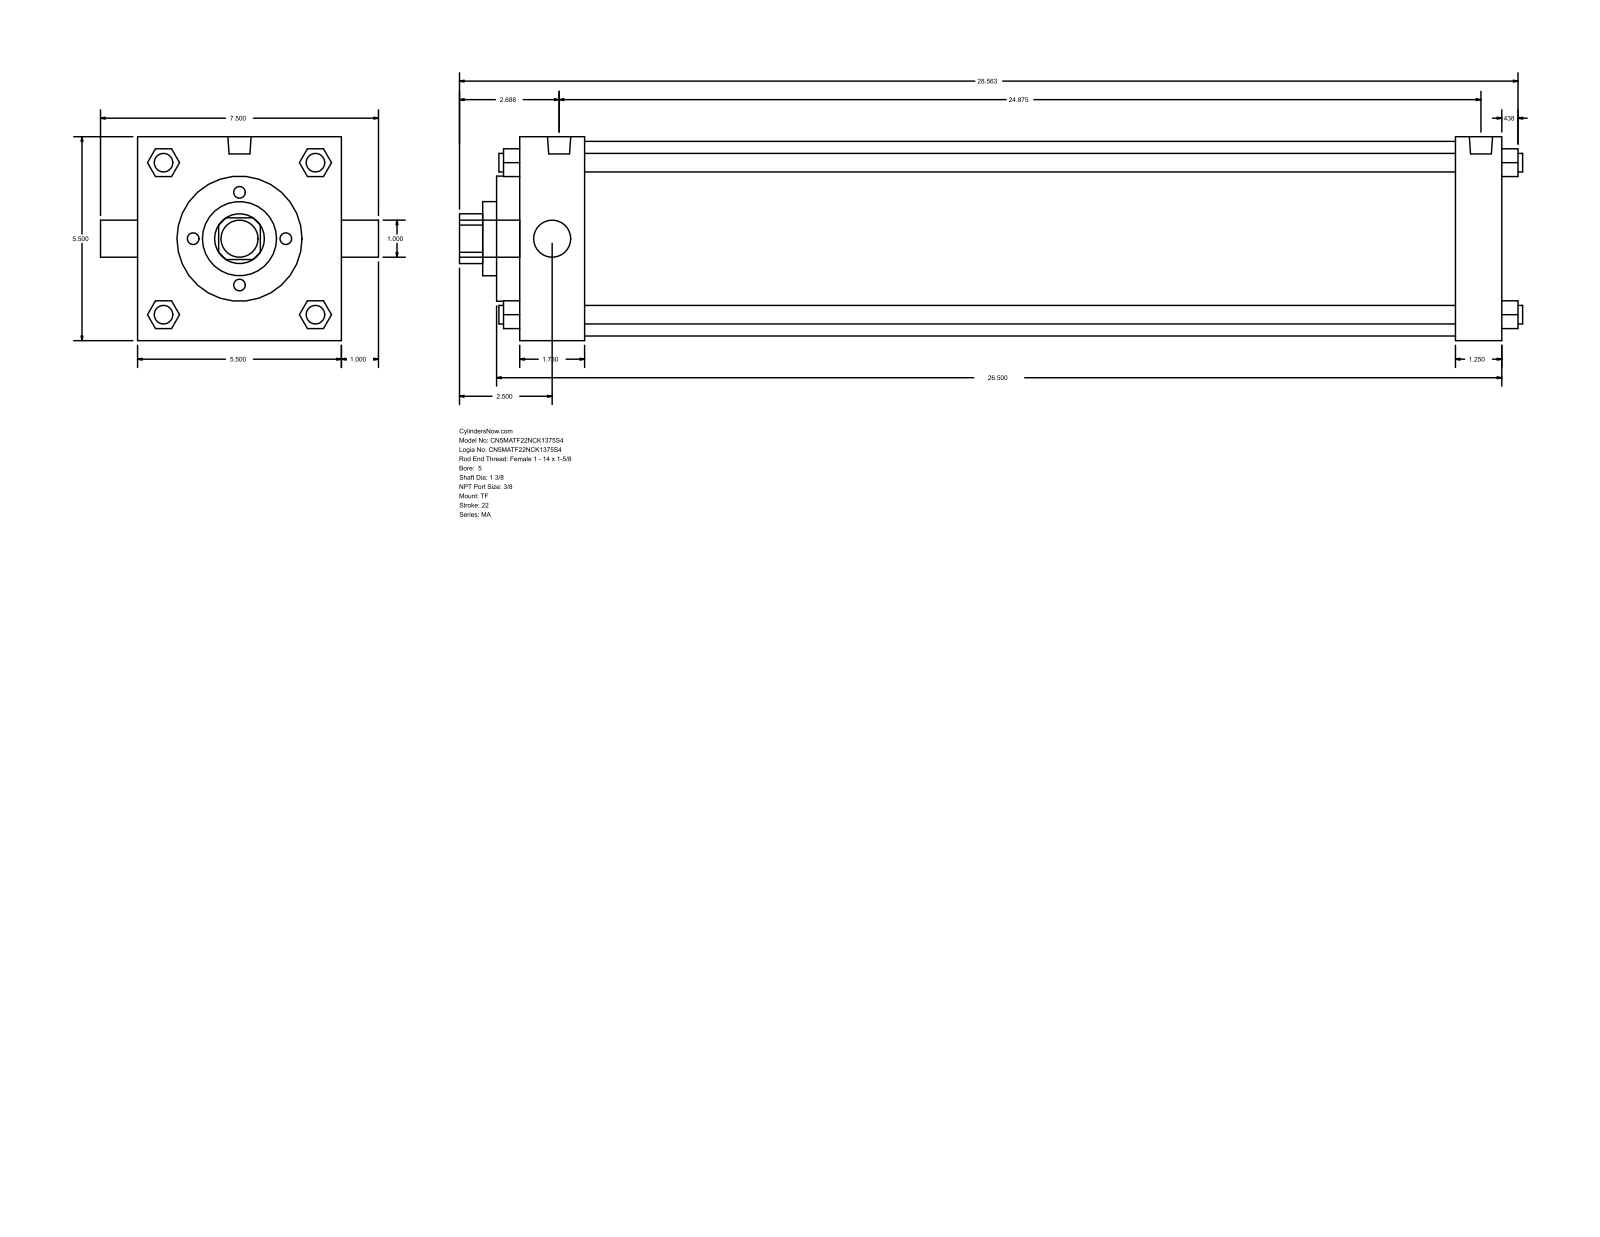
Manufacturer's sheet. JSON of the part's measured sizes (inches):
{"part_name": "MA_TF__0500_1.375", "step_written_by": "GSSL Pune (CONFIG_CONTROL_DESIGN)", "units": "inches", "bodies": {"solids": 0, "faces": 122, "planar": 93, "cylindrical": 29, "other": 0}, "overall_size": [28.687, 7.5, 5.5], "round_holes": [[1, 1], [1.375, 1], [2, 1], [3.375, 1], [5.25, 1]], "round_bosses_or_shafts": [[0.5, 4], [0.437, 3], [0.627, 2], [1, 1]], "partial_cylinders_radius": [[0.672, 1]], "face_to_face_distances": [5.5, 26.5, 25.25, 1.25, 1.75, 23.5, 24.75, 0.625, 2.375, 25.875]}
